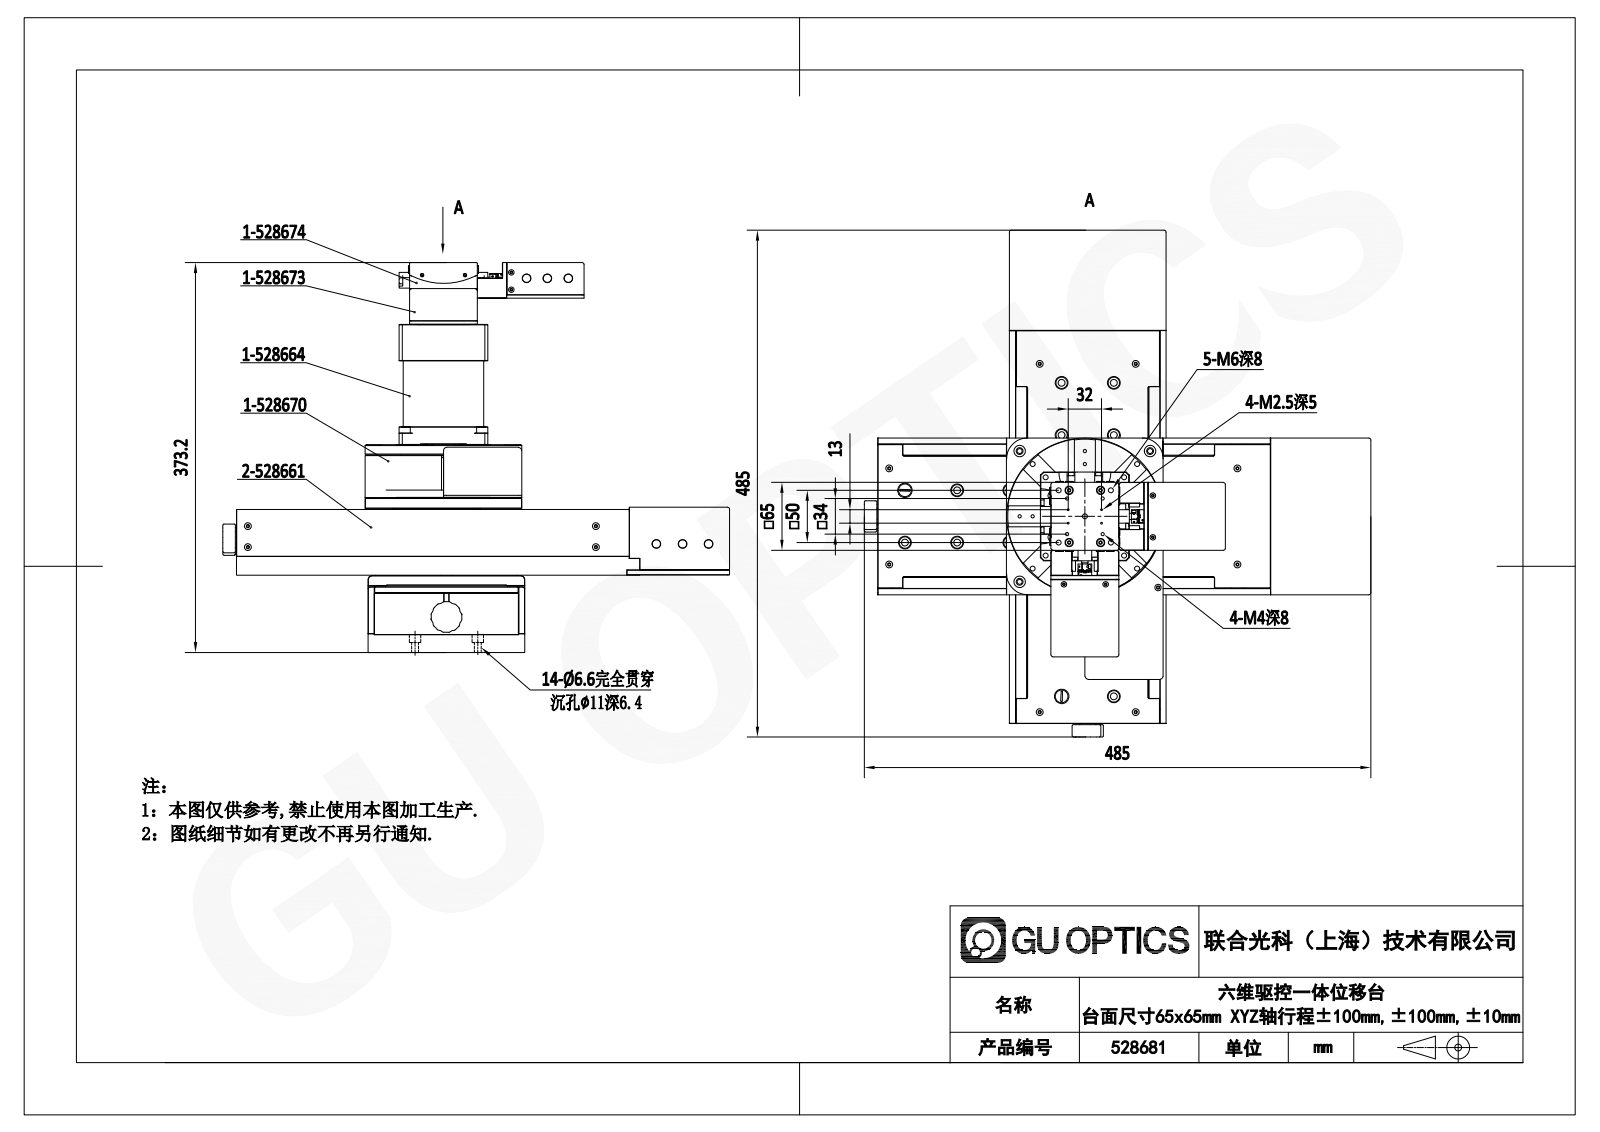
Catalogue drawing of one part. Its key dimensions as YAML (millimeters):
part_name: "528681; 528664; 528674; 528673 (+2 more)"
step_written_by: "SolidWorks 2020 (CONFIG_CONTROL_DESIGN)"
units: millimeters
bodies: {solids: 227, faces: 9437, planar: 5710, cylindrical: 2239, other: 1488}
overall_size: [485, 485, 373.2]
volume: 7136000
surface_area: 2092000
round_holes:
  - {diameter: 5, count: 102}
  - {diameter: 3.3, count: 93}
  - {diameter: 2.5, count: 90}
  - {diameter: 3.4, count: 86}
  - {diameter: 6.5, count: 73}
  - {diameter: 11, count: 59}
  - {diameter: 6.6, count: 55}
  - {diameter: 8, count: 38}
  - {diameter: 4.5, count: 36}
  - {diameter: 3.5, count: 34}
  - {diameter: 2.05, count: 30}
  - {diameter: 12.5, count: 28}
round_bosses_or_shafts:
  - {diameter: 2, count: 36}
  - {diameter: 4, count: 20}
  - {diameter: 3, count: 18}
  - {diameter: 7, count: 16}
  - {diameter: 7.5, count: 8}
  - {diameter: 5.5, count: 8}
  - {diameter: 2.5, count: 8}
  - {diameter: 2.4, count: 8}
partial_cylinders:
  - {radius: 2, count: 153}
  - {radius: 1, count: 57}
  - {radius: 5, count: 49}
  - {radius: 3, count: 35}
  - {radius: 4, count: 19}
  - {radius: 7.5, count: 18}
  - {radius: 2.5, count: 13}
  - {radius: 1.35, count: 8}
face_to_face_distances: [74, 6, 57, 18, 39, 63, 17, 45, 144, 150]
hole_center_spacings: [12.5, 62.5, 25, 37.5, 50, 27.95, 39.53, 51.54]
